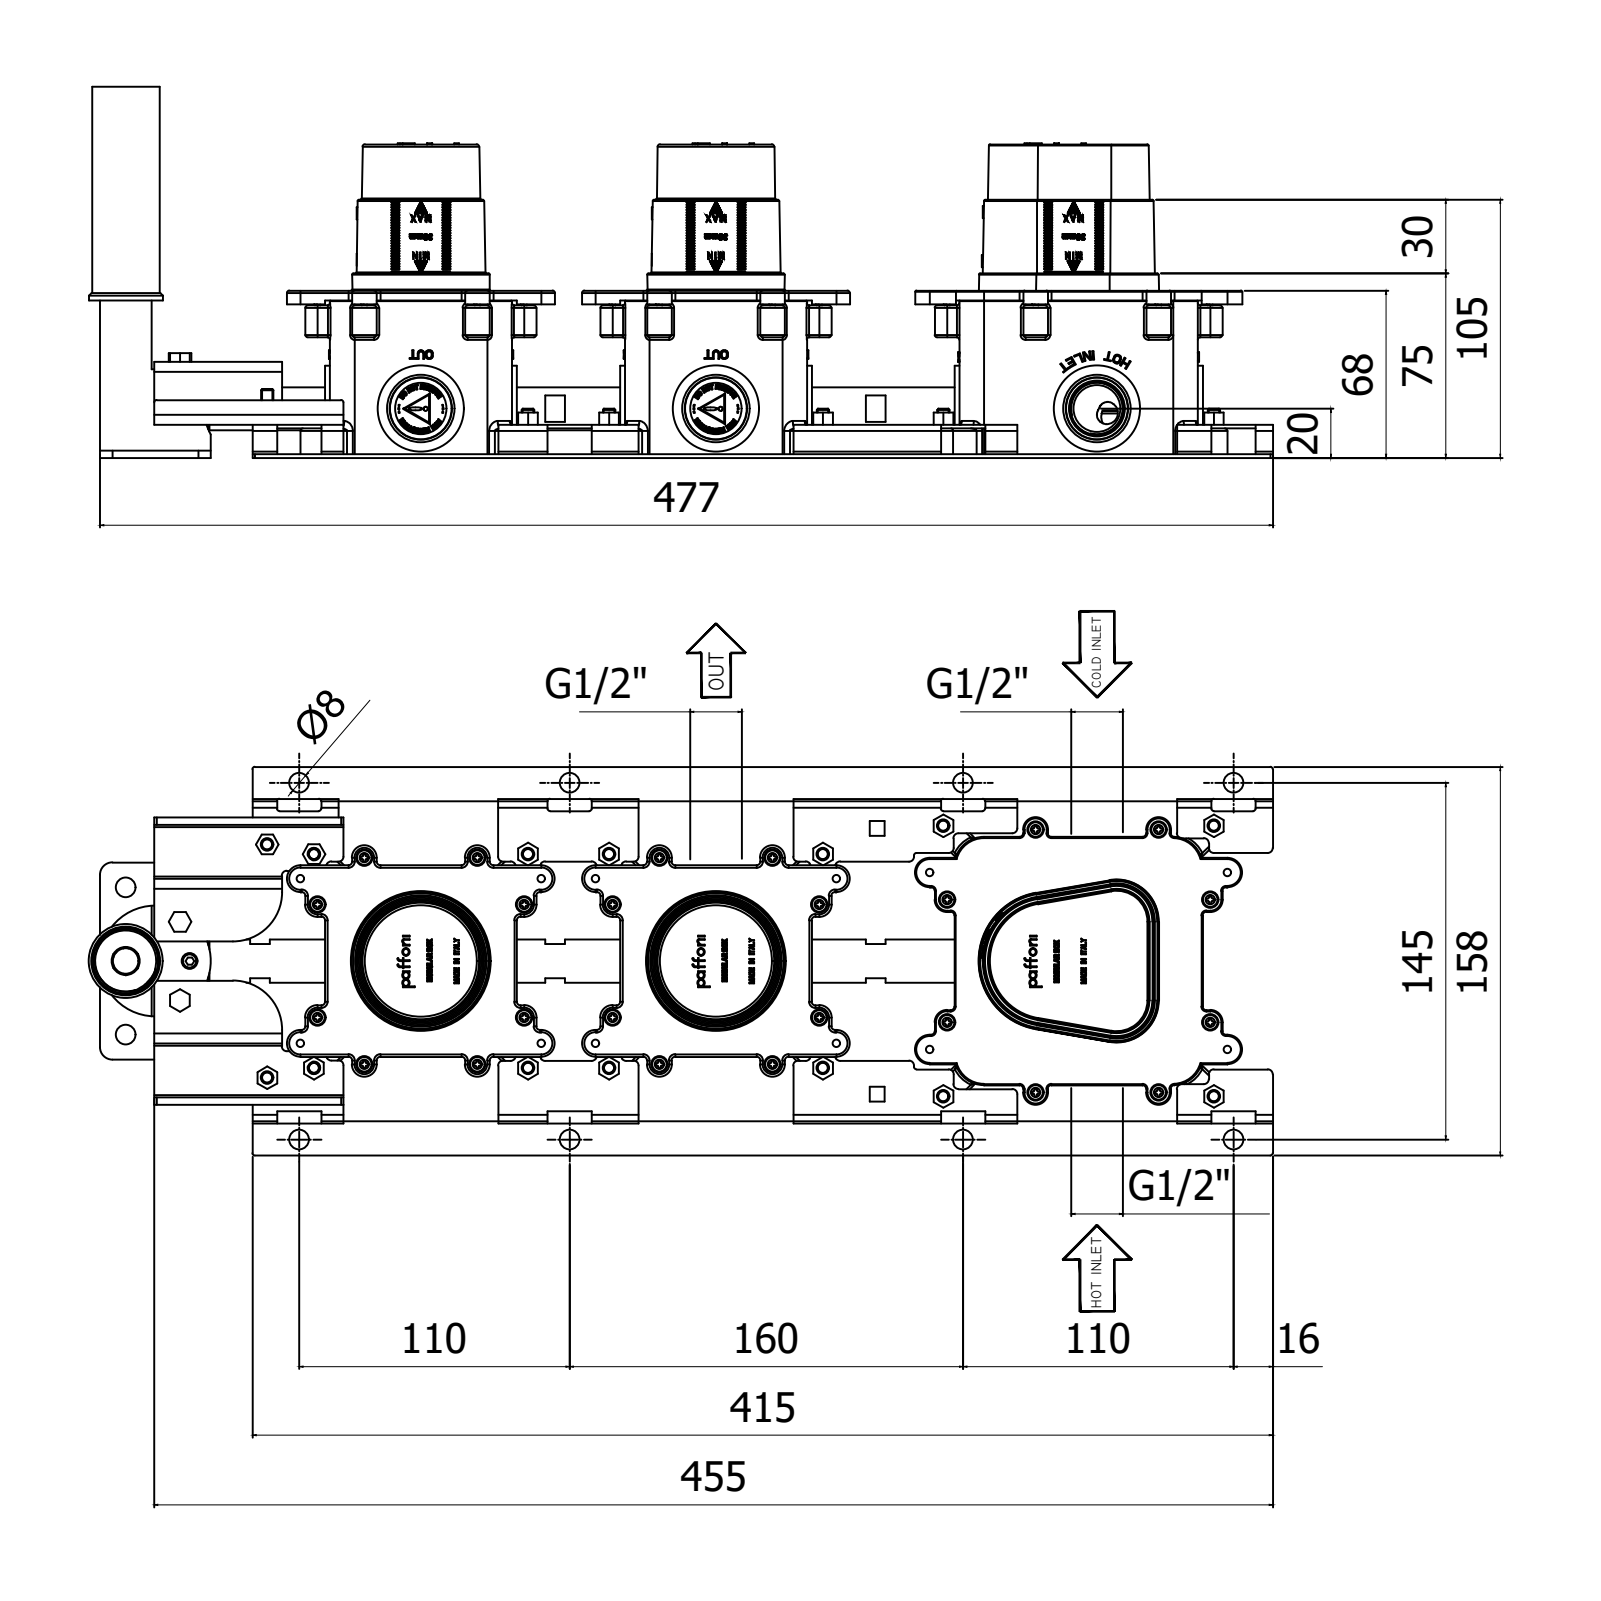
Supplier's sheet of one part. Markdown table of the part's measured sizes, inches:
| quantity | value |
| --- | --- |
| part name | MDBOX000 |
| STEP written by | CREO PARAMETRIC BY PTC INC, 2020044 (CONFIG_CONTROL_DESIGN) |
| units | inches |
| bodies | 4 solids, 15441 faces (8431 planar, 3901 cylindrical, 3109 other) |
| overall size | 18.947 × 6.22 × 5.039 |
| volume | 53.65 in³ |
| surface area | 876.6 in² |
| round holes (diameter × count) | 0.098 × 24, 0.138 × 24, 0.26 × 24, 0.315 × 14, 0.118 × 12, 0.165 × 6, 0.354 × 6, 0.394 × 6, 0.748 × 5, 0.059 × 4, 1 × 4, 0.13 × 3 |
| round bosses / shafts (diameter × count) | 0.232 × 24, 0.082 × 24, 0.197 × 15, 1.378 × 4, 1.024 × 4, 1.567 × 3, 1.496 × 3, 0.984 × 3 |
| partial cylindrical surfaces (radius × count) | 0.039 × 212, 0.02 × 166, 0.012 × 108, 0.008 × 92, 0.059 × 62, 0.006 × 60, 0.079 × 60, 0.118 × 54 |
| main face-to-face distances | 0.079, 0.059, 0.453, 2.598, 0.472, 0.02, 2.677, 0.531, 2.52, 2.343 |
| hole center spacings | 2.666, 4.724, 1.058, 1.811, 1.885, 3.307, 3.619, 3.77 |
